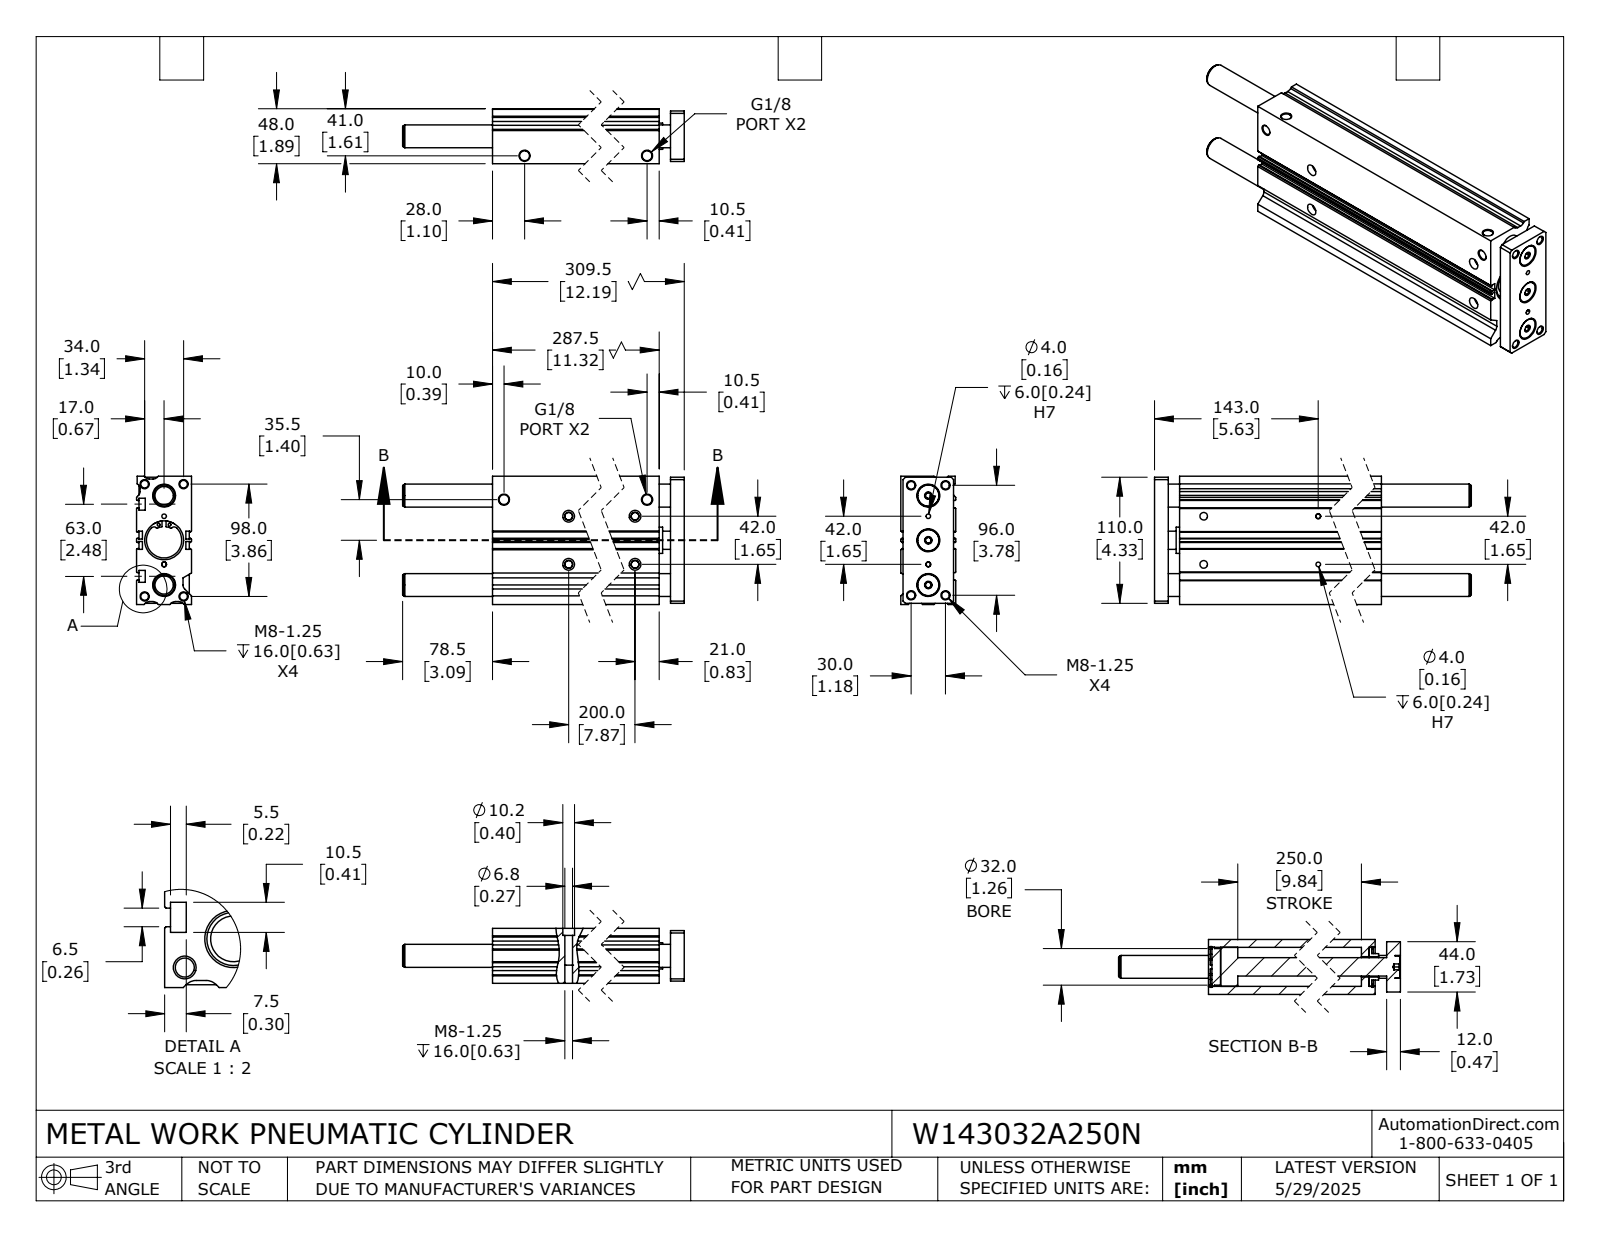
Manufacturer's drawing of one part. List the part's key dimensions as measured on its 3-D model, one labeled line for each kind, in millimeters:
Part name (STEP PRODUCT): W143032A250N; W143032A250N_BODY; W143032A250N_ROD
STEP written by: SolidWorks 2024 (CONFIG_CONTROL_DESIGN)
Units: millimetres
Bodies: 6 solids, 394 faces (195 planar, 149 cylindrical, 50 other)
Overall size (bounding box): 388 × 112 × 48
Volume: 1 328 000 mm³ · Surface area: 290 200 mm²
Round holes (diameter × count): ⌀6.7 ×12, ⌀2.5 ×4, ⌀4 ×4, ⌀6.8 ×4, ⌀8.6 ×4, ⌀10.2 ×4, ⌀5 ×3, ⌀20 ×3, ⌀17.7 ×1, ⌀30.8 ×1
Round bosses / shafts (diameter × count): ⌀19 ×3, ⌀35.7 ×2, ⌀34 ×1, ⌀32 ×1, ⌀23 ×1, ⌀16 ×1
Partial cylindrical surfaces — rounded edges, fillets, slot ends (radius × count): R5 ×9, R2 ×4, R3 ×4, R12.9 ×2
Main face-to-face distances: 48, 2.5, 7.5, 43, 5, 40.5, 3, 112, 2, 35.5
Hole centre spacings: 2.2, 8.8, 14.4, 17.5, 19.7, 25.9, 30.9, 32
